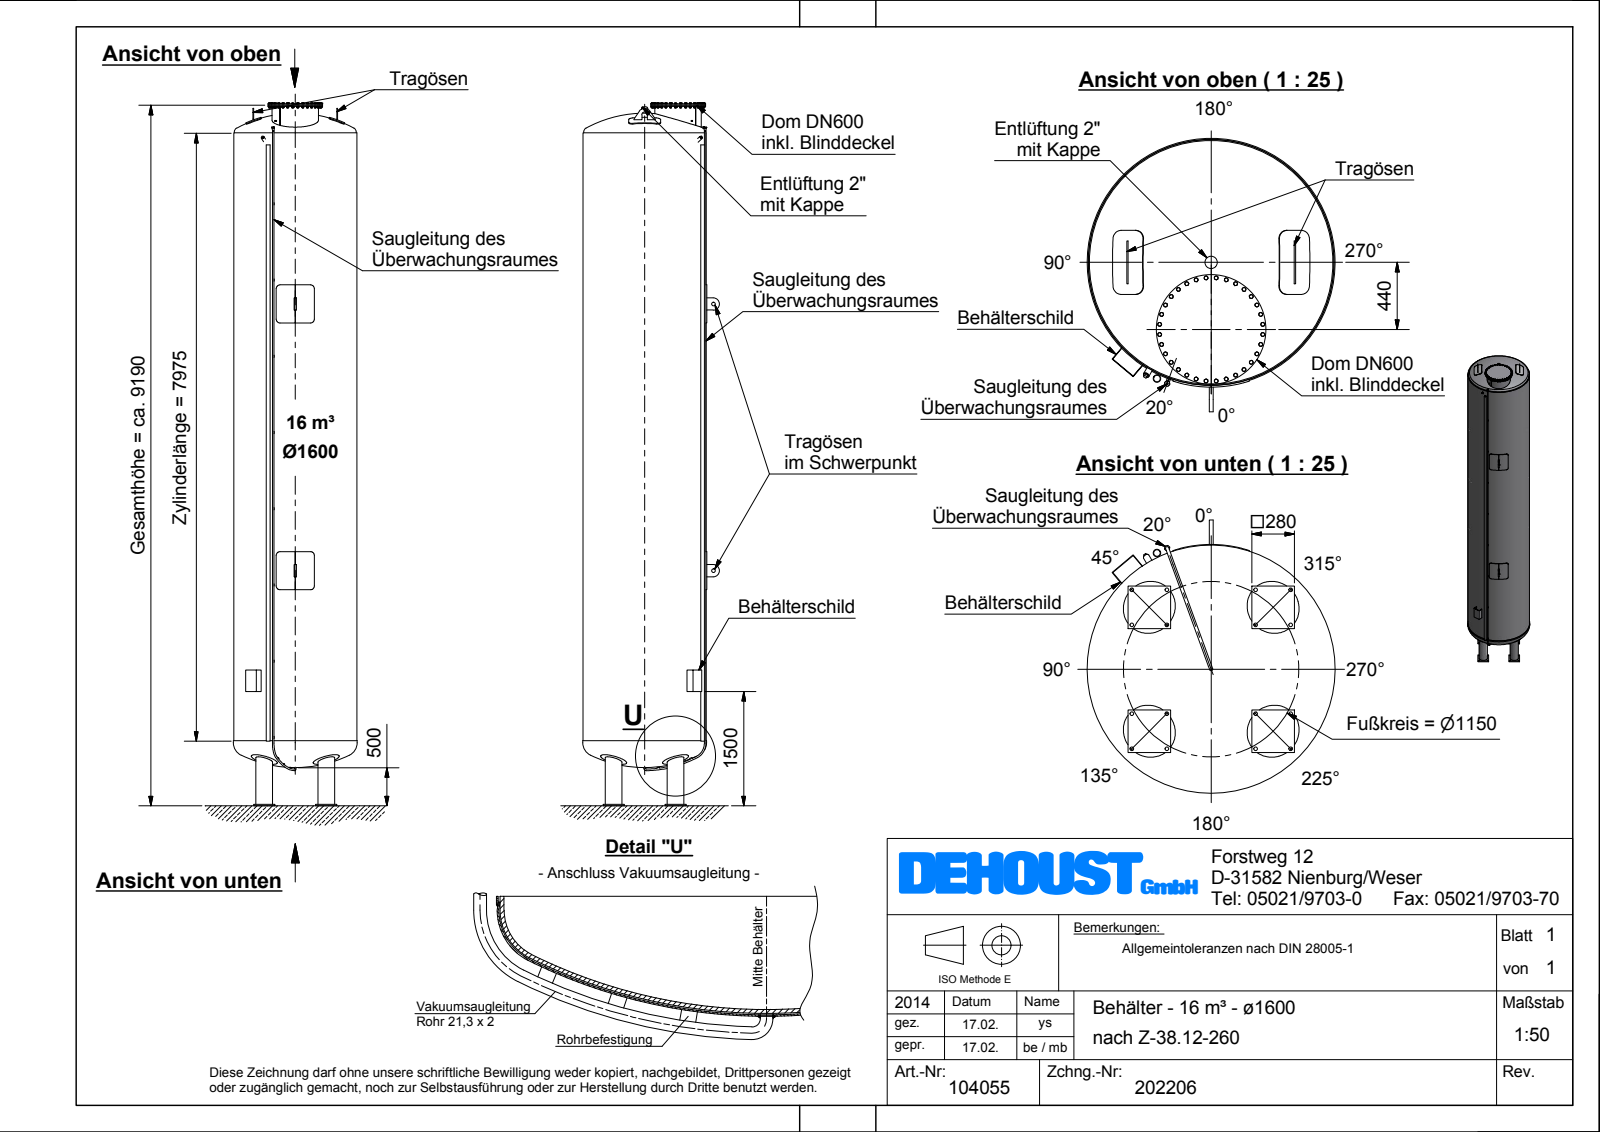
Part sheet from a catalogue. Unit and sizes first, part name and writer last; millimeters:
Units: millimetres
Overall size (bounding box): 9219.34 × 1721.38 × 1626
Round holes (diameter × count): ⌀203.1 ×4, ⌀598 ×1, ⌀1590 ×1
Round bosses / shafts (diameter × count): ⌀22.5 ×32, ⌀16 ×32, ⌀350 ×4, ⌀219.1 ×4, ⌀21.3 ×2, ⌀1626 ×1, ⌀1616 ×1, ⌀1600 ×1
Partial cylindrical surfaces — rounded edges, fillets, slot ends (radius × count): R50 ×8, R56 ×8, R35 ×2, R80 ×2, R85 ×2, R818 ×1
Main face-to-face distances: 379.69, 344.69, 35, 8829.65, 9174.34, 9209.34, 20, 9154.34, 8809.65, 9189.34
Hole centre spacings: 575, 813.17, 407.96, 939.16, 1150, 440
Volume: 16 940 000 000 mm³ · Surface area: 57 700 000 mm²
Bodies: 12 solids, 1218 faces (736 planar, 158 cylindrical, 324 other)
Part name (STEP PRODUCT): Z-38_12-260_Beh\S\dlter_\S\x1600_016m\S\3_Dichte=1,0
STEP written by: Autodesk Inventor 2012 (AUTOMOTIVE_DESIGN)
